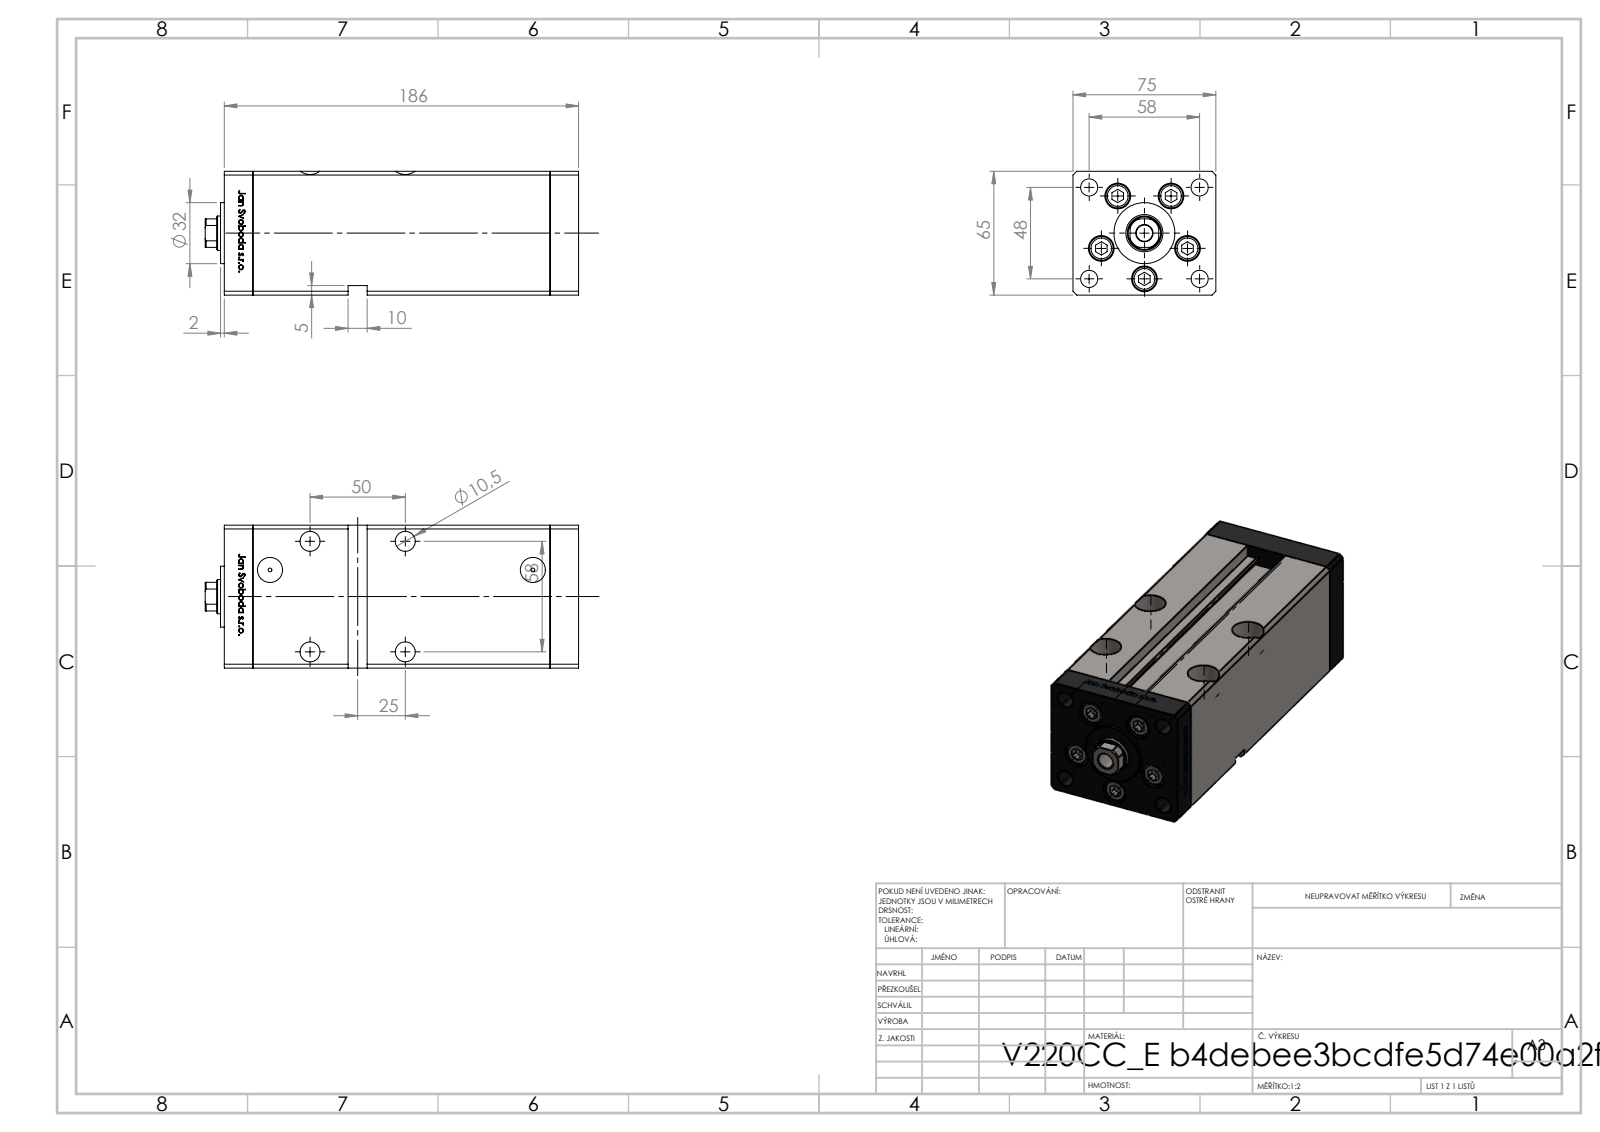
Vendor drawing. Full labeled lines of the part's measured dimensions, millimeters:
Part name (STEP PRODUCT): V220C_VC_E; V220C_FRONT_E; V220C BACK_E; V220C_E MIDDLE (+1 more)
STEP written by: SolidWorks 2019 (CONFIG_CONTROL_DESIGN)
Units: millimetres
Bodies: 14 solids, 1212 faces (473 planar, 165 cylindrical, 574 other)
Overall size (bounding box): 196 × 75 × 65
Volume: 769 603 mm³ · Surface area: 146 638 mm²
Round holes (diameter × count): ⌀9 ×9, ⌀13.5 ×5, ⌀10.5 ×4, ⌀16.5 ×4, ⌀2 ×2, ⌀13.16 ×2, ⌀8.5 ×1, ⌀18 ×1, ⌀19.5 ×1
Round bosses / shafts (diameter × count): ⌀12.5 ×5, ⌀8 ×5, ⌀32 ×1
Partial cylindrical surfaces — rounded edges, fillets, slot ends (radius × count): R0.93 ×2, R8.5 ×1
Main face-to-face distances: 75, 65, 15, 156, 171, 186, 28, 54.5, 10.5, 26.25
Hole centre spacings: 24, 37.64, 58, 15.67, 17.22, 27.71, 28.83, 29
